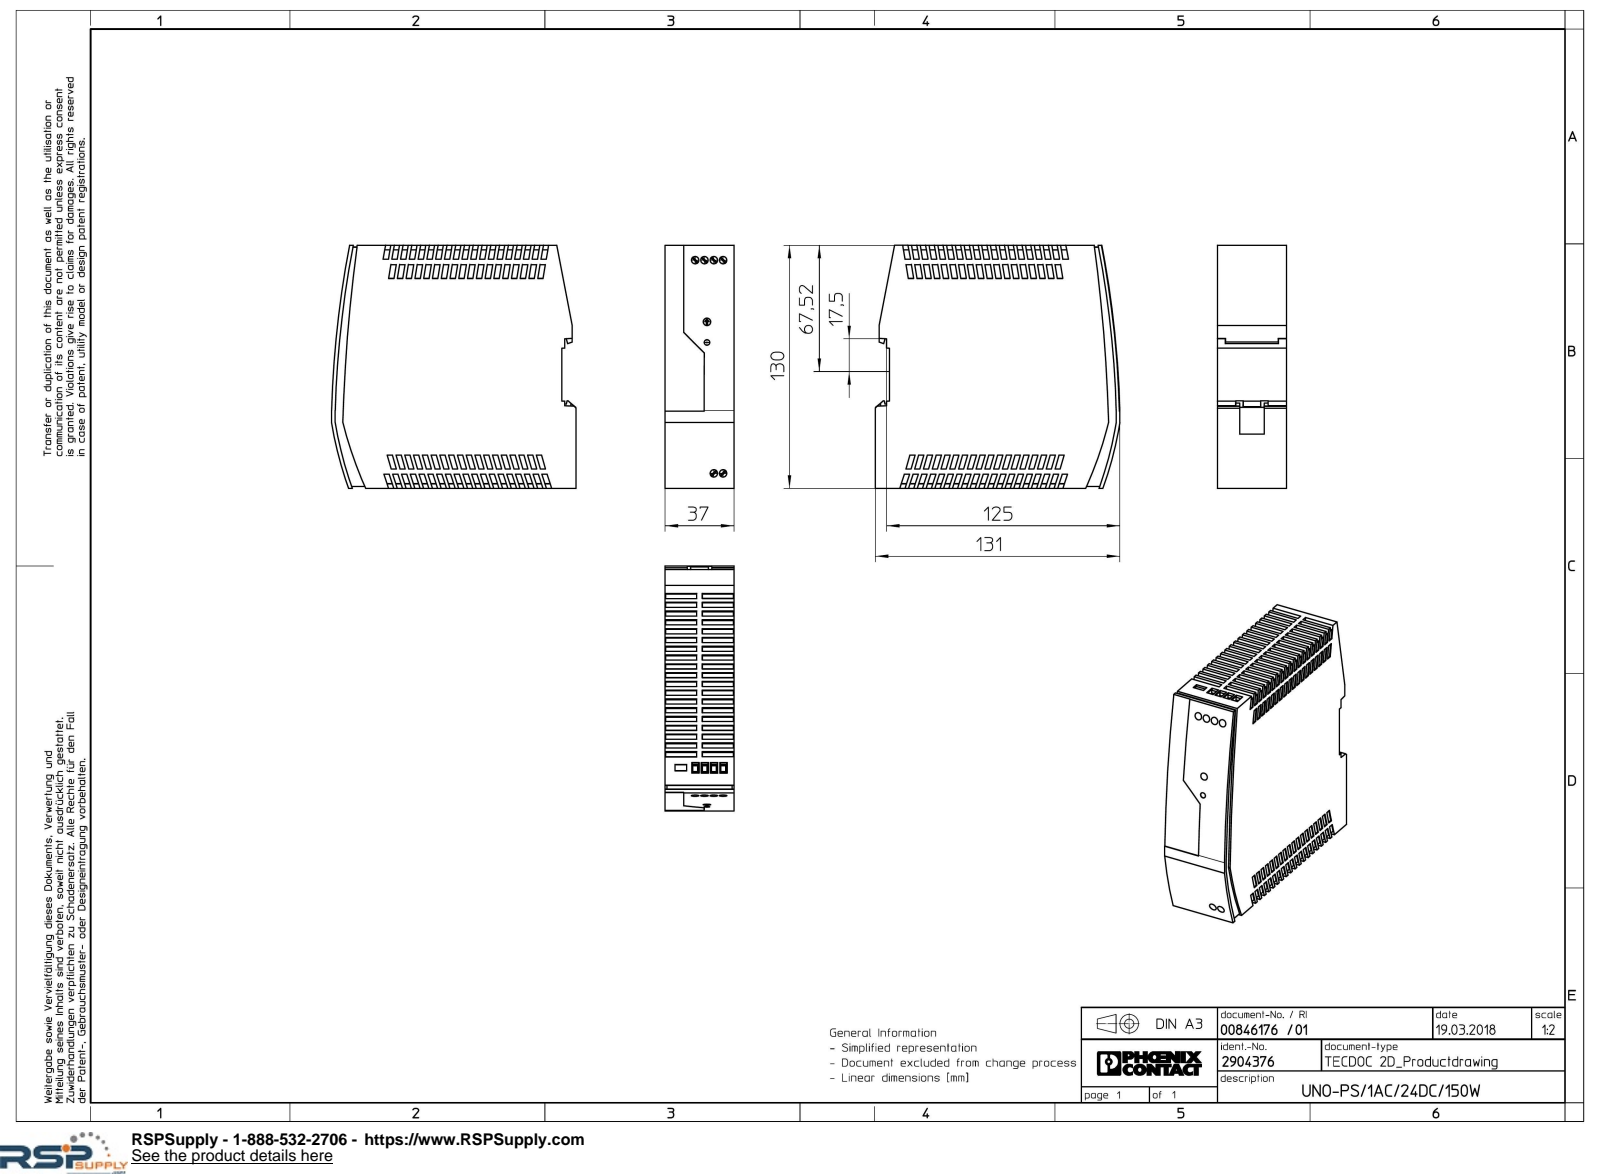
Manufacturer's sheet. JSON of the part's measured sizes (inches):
{"part_name": "UNO_PS_1AC_24DC_150W-select", "step_written_by": "Creo Elements/Direct Modeling 18.1I 14-Aug-2016 (C) Parametric Technology GmbH (AUTOMOTIVE_DESIGN)", "units": "inches", "bodies": {"solids": 1, "faces": 1071, "planar": 818, "cylindrical": 246, "other": 7}, "overall_size": [5.157, 5.118, 1.457], "volume_in3": 35.42, "surface_area_in2": 93.47, "round_holes": [[0.157, 7], [0.118, 1]], "partial_cylinders_radius": [[11.811, 38], [21.654, 20], [11.81, 18], [11.812, 18], [21.653, 18], [21.654, 5], [7.797, 1], [7.872, 1]], "face_to_face_distances": [1.457, 0.098, 5.02, 0.016, 1.441, 5.118, 4.921, 0.039, 1.425, 1.417], "hole_center_spacings": [0.197, 4.493, 0.394, 4.488, 4.506, 0.433, 0.591, 1.3]}
